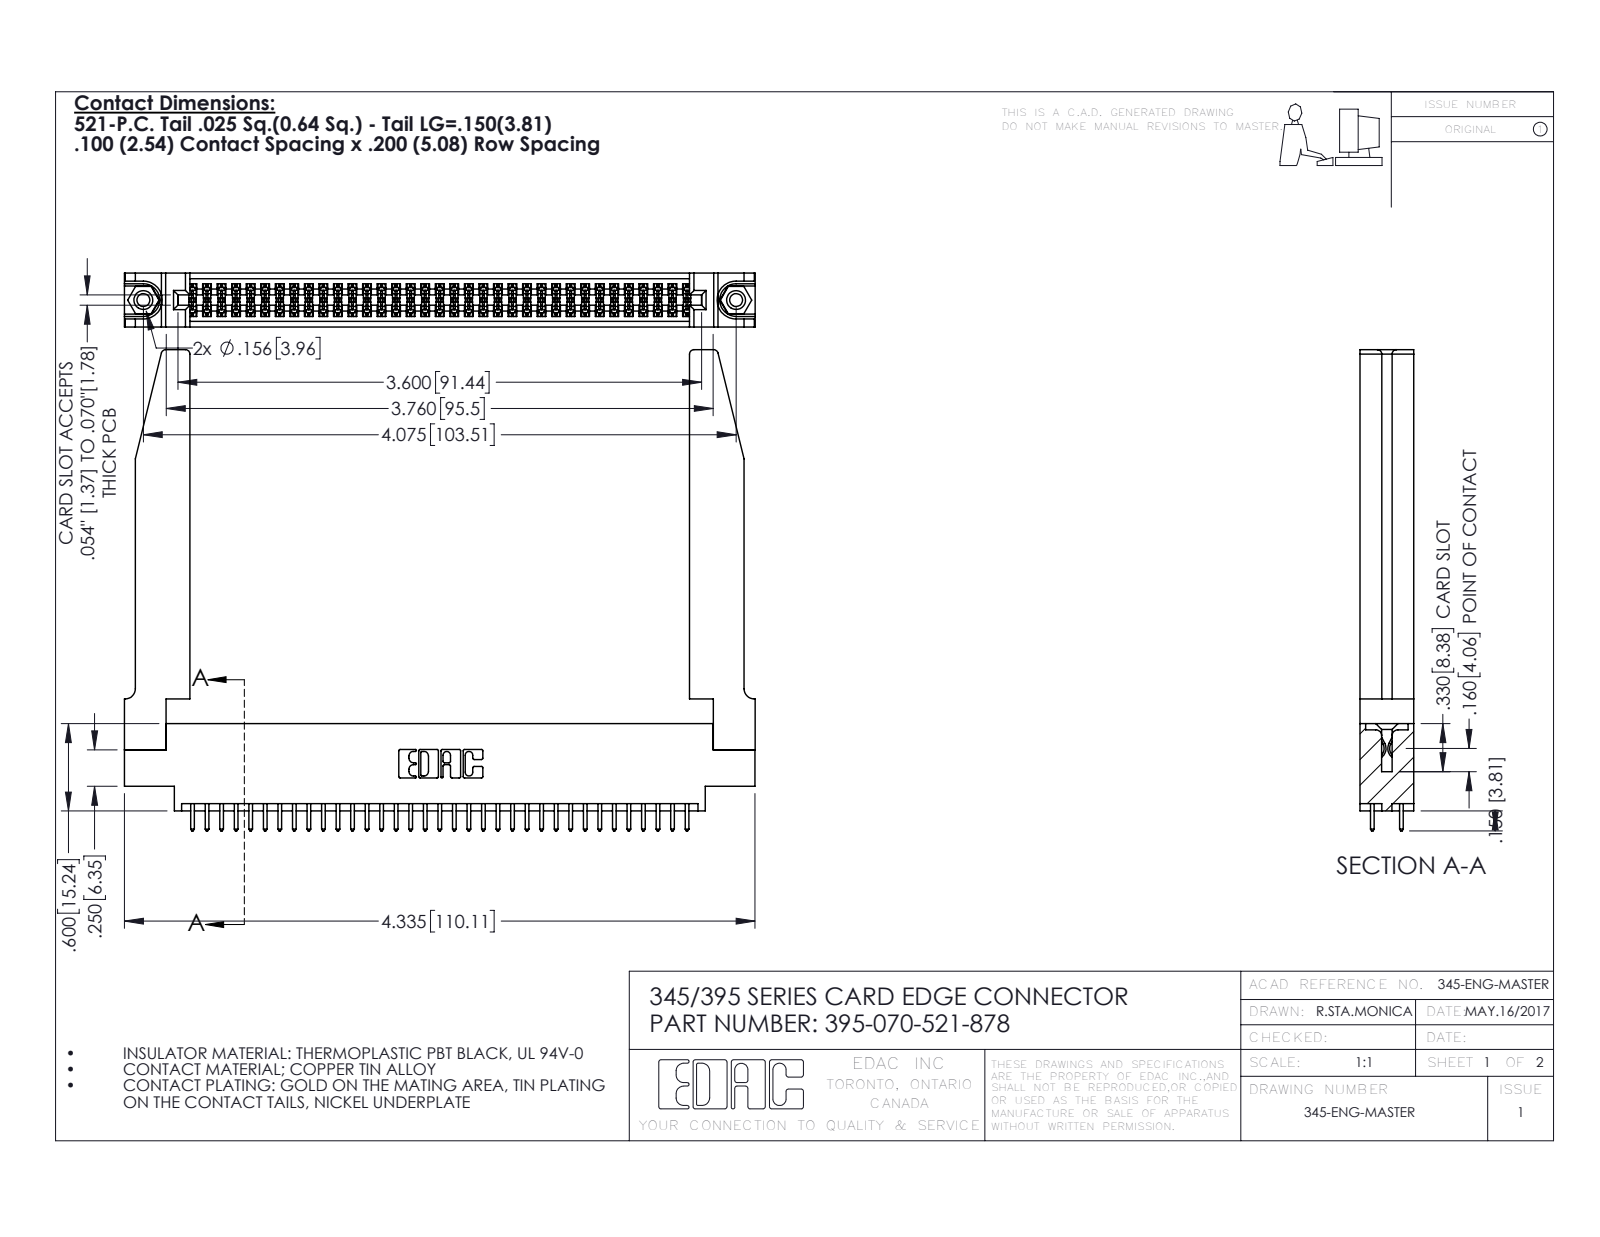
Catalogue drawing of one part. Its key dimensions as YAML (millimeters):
part_name: "345-250-001_345-250-001-102; 345-220-078_345-220-078; 395-070-521-878; 345 Part_0.170 Offset - 0.156 Dia-TH (+1 more)"
step_written_by: "SolidWorks 2016 (CONFIG_CONTROL_DESIGN)"
units: millimeters
bodies: {solids: 75, faces: 3864, planar: 2536, cylindrical: 1276, other: 52}
overall_size: [110.1, 84, 9.4]
volume: 18260
surface_area: 22170
round_holes:
  - {diameter: 2.3, count: 2}
  - {diameter: 3.2, count: 2}
  - {diameter: 4, count: 2}
  - {diameter: 1.6, count: 1}
round_bosses_or_shafts:
  - {diameter: 3.9, count: 2}
partial_cylinders:
  - {radius: 0.2, count: 105}
  - {radius: 0.3, count: 70}
  - {radius: 0.3, count: 22}
  - {radius: 0.8, count: 8}
  - {radius: 0.2, count: 6}
  - {radius: 0.8, count: 6}
  - {radius: 0.7, count: 3}
  - {radius: 0.4, count: 2}
face_to_face_distances: [9.4, 1.8, 7.6, 2.5, 6.9, 0.6, 5.1, 5.7, 4.4, 3.8]
hole_center_spacings: [6.9, 97.5, 103.5]
